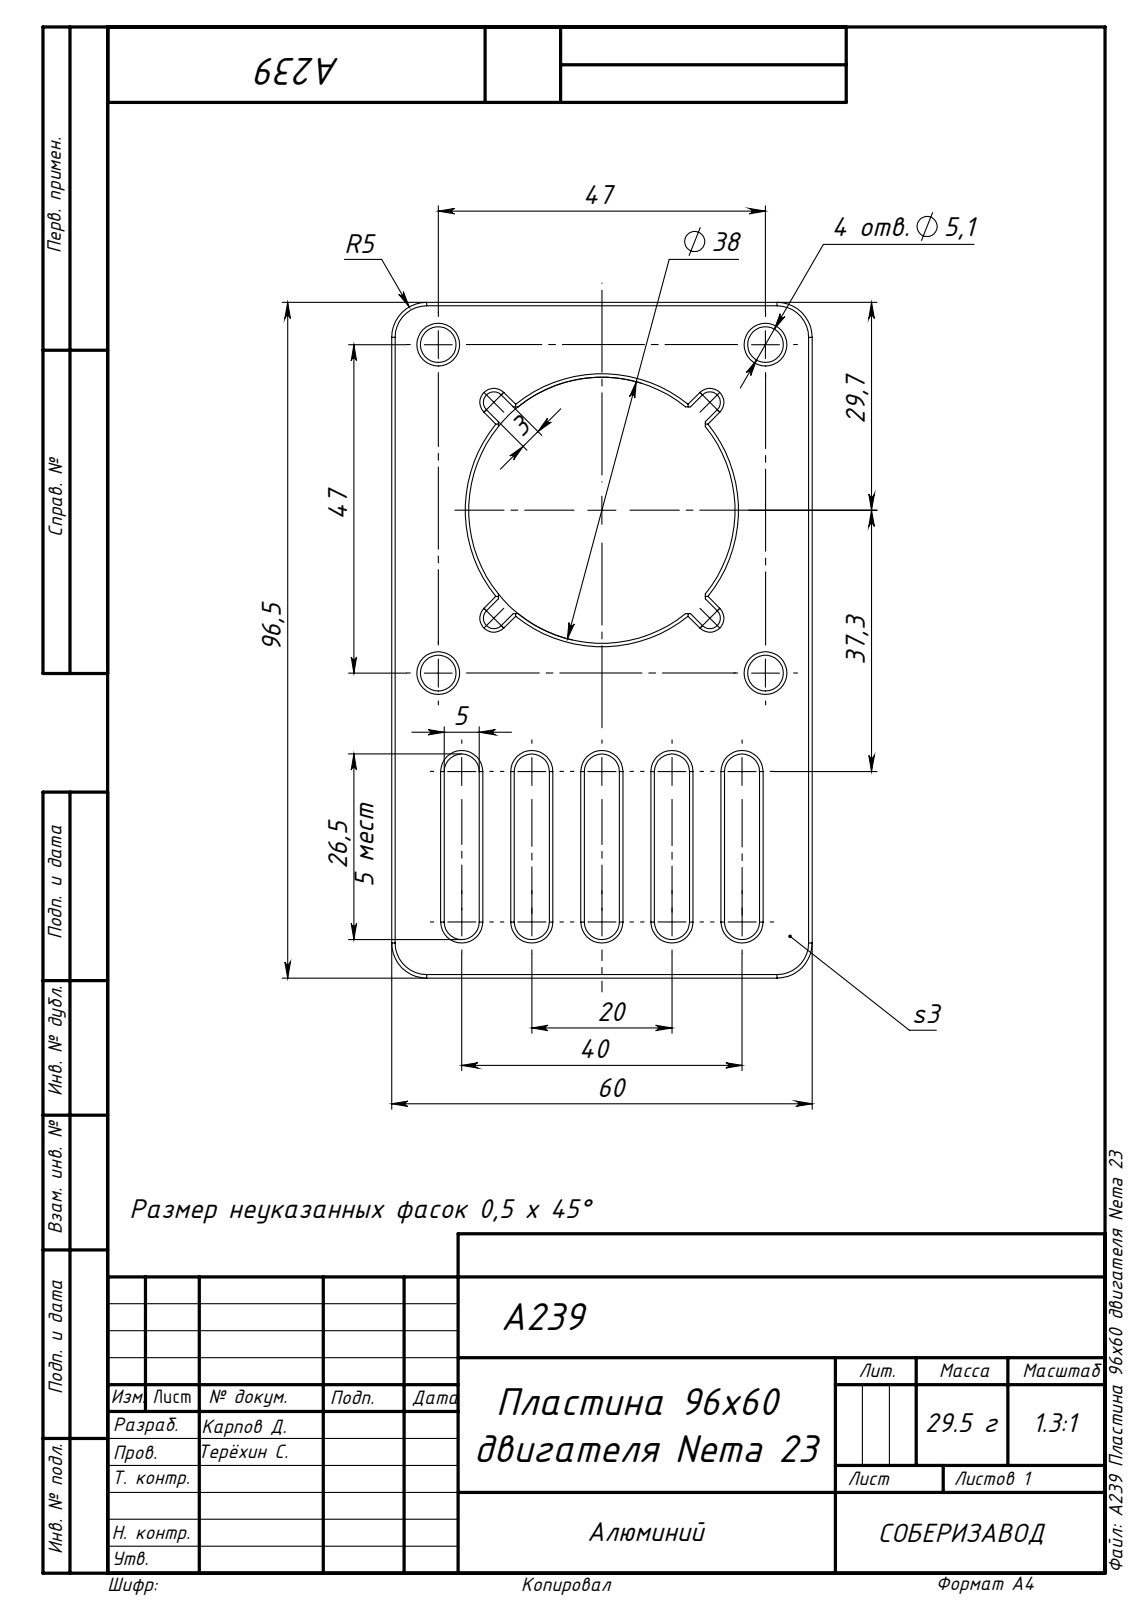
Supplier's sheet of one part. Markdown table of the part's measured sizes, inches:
| quantity | value |
| --- | --- |
| part name | A239 Пластина 96x60 двигателя Nema 23 |
| STEP written by | SolidWorks 2018 (AUTOMOTIVE_DESIGN) |
| units | inches |
| bodies | 1 solid, 130 faces (54 planar, 38 cylindrical, 38 other) |
| overall size | 3.799 × 2.362 × 0.118 |
| volume | 0.702 in³ |
| surface area | 15.39 in² |
| round holes (diameter × count) | 0.201 × 4, 1.496 × 1 |
| partial cylindrical surfaces (radius × count) | 0.098 × 10, 0.059 × 4, 0.197 × 4 |
| main face-to-face distances | 0.118, 0.197, 0.394, 0.591, 0.787, 0.984, 2.362, 1.181, 1.378, 3.799 |
| hole center spacings | 1.297, 1.308, 1.839, 1.846, 2.606 |
